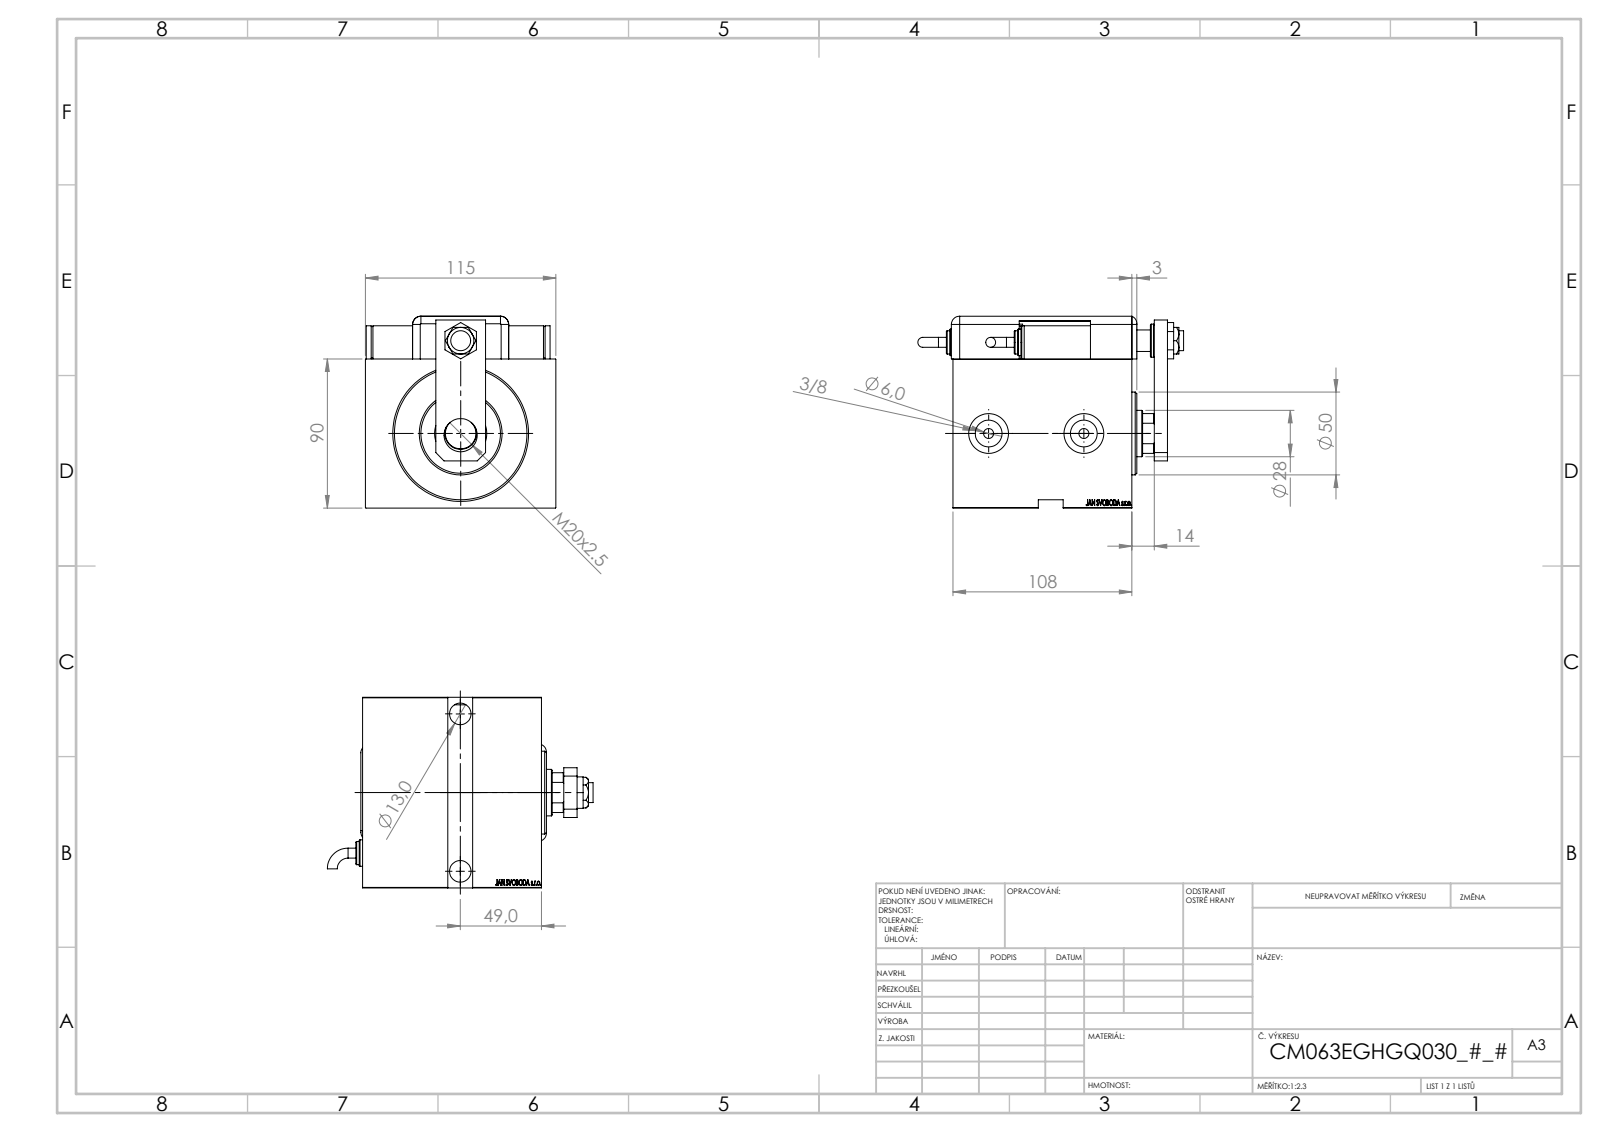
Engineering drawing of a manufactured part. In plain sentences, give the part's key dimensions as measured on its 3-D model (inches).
The part is named "MAGNETIC SWITCH Q; NUT_D13; V450CM_E_Body; TYC (+7 more)". Its 3-D file was written by "SolidWorks 2019 (CONFIG_CONTROL_DESIGN)". It is 13 solids with 1234 faces: 616 planar, 101 cylindrical and 517 other. Overall it measures 6.317 by 4.559 by 4.528 inches. Its volume is 68.1 cubic inches and its surface area 286.5 square inches. Round holes: 3 of diameter 0.512, 2 of diameter 0.157, 2 of diameter 0.236, 2 of diameter 0.315, 2 of diameter 0.637, 2 of diameter 0.748, 2 of diameter 0.945, 1 of diameter 0.472, 1 of diameter 0.551, 1 of diameter 0.728, 1 of diameter 0.787, 1 of diameter 1.102. Round bosses or shafts: 3 of diameter 0.787, 2 of diameter 0.63, 2 of diameter 0.551, 2 of diameter 0.236, 1 of diameter 1.969. Partial cylindrical surfaces (rounded edges, fillets, slot ends): 9 of radius 0.197, 1 of radius 0.394, 1 of radius 0.531. The main face-to-face distances are 4.252, 0.118, 3.543, 4.528, 0.748, 3.504, 4.559, 1.016, 0.197, 0.11. The hole center spacings are 2.202, 2.792, 0.039, 0.787, 2.205, 2.244, 2.264, 3.74.
